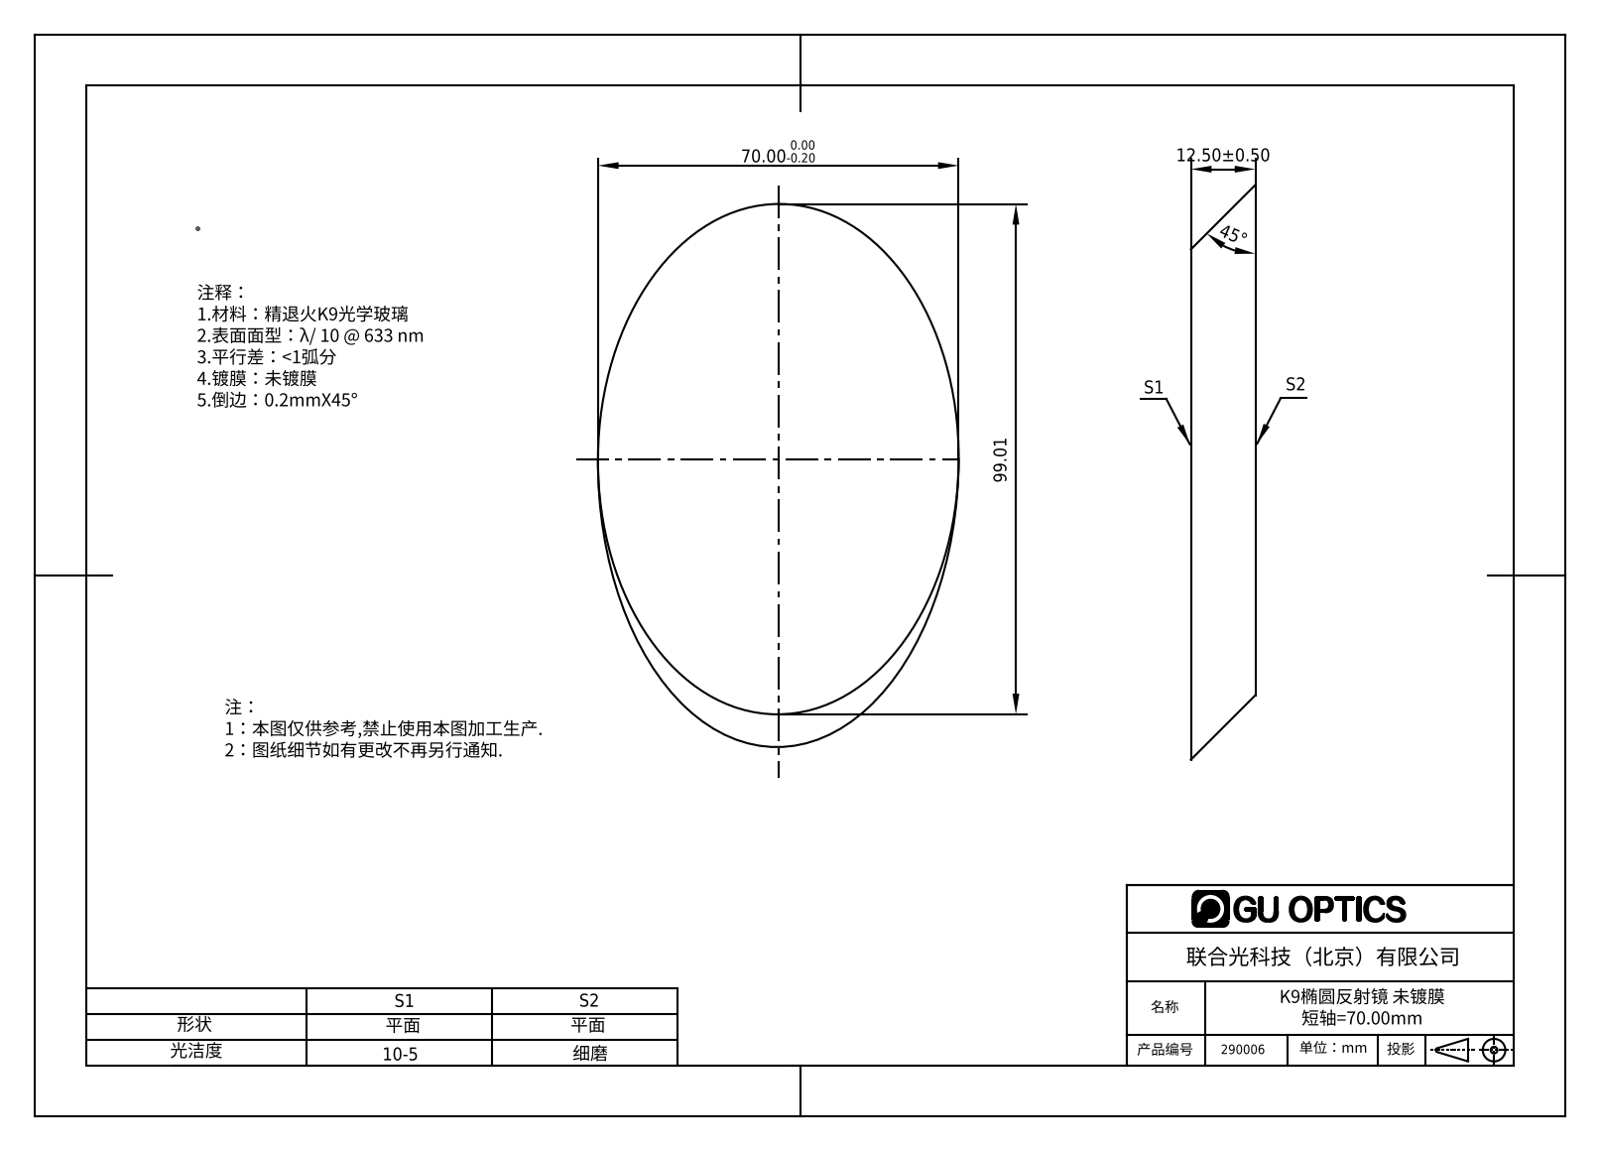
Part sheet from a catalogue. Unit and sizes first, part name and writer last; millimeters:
Units: millimetres
Overall size (bounding box): 111.51 × 70 × 12.5
Main face-to-face distances: 12.5
Volume: 68 047 mm³ · Surface area: 14 773 mm²
Bodies: 1 solid, 4 faces (2 planar, 0 cylindrical, 2 other)
Part name (STEP PRODUCT): 290006
STEP written by: SolidWorks 2016 (AUTOMOTIVE_DESIGN)
